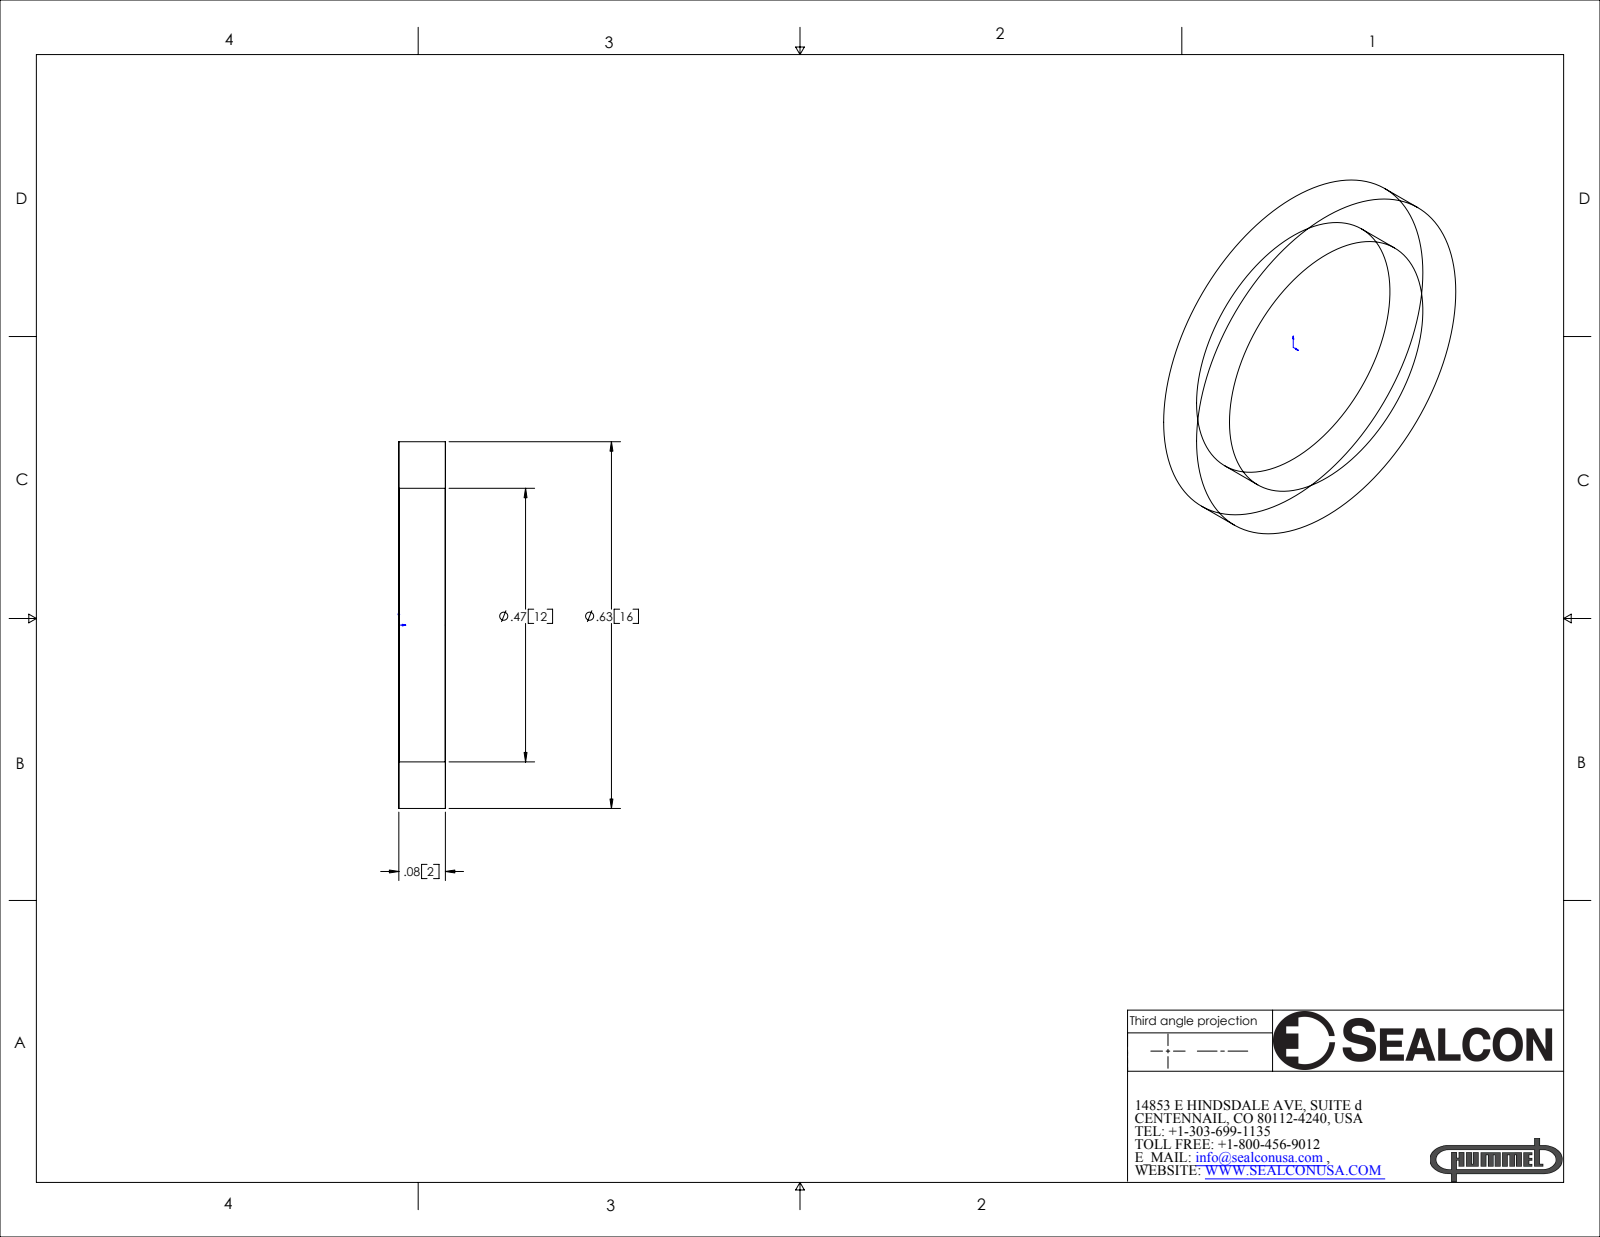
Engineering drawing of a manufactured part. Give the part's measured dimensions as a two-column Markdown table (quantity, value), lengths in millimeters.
| quantity | value |
| --- | --- |
| part name | MS-12-NY |
| STEP written by | SolidWorks 2007 (CONFIG_CONTROL_DESIGN) |
| units | millimeters |
| bodies | 1 solid, 6 faces (2 planar, 4 cylindrical, 0 other) |
| overall size | 16 × 16 × 2 |
| volume | 180 mm³ |
| surface area | 357 mm² |
| round holes (diameter × count) | 11.9 × 1 |
| round bosses / shafts (diameter × count) | 16 × 1 |
| main face-to-face distances | 2 |
